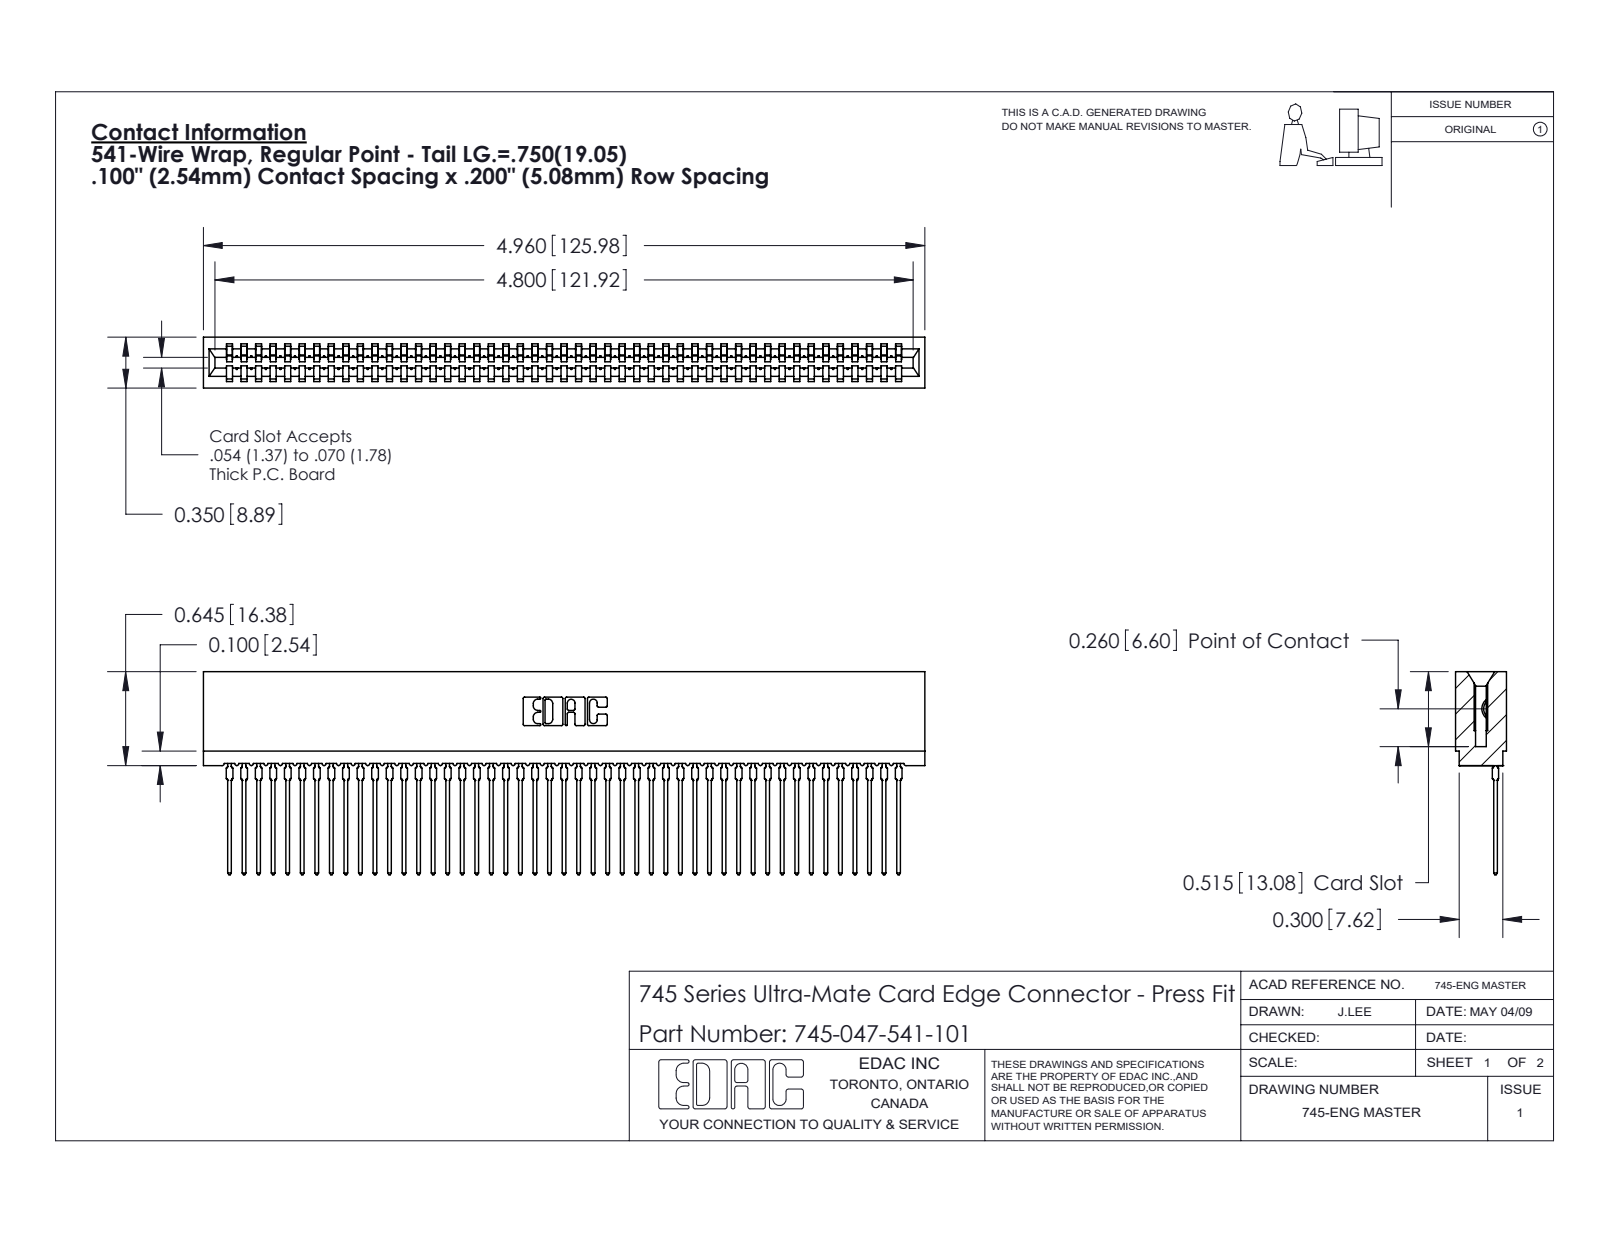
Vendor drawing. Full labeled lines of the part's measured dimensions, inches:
Part name (STEP PRODUCT): 745-047-541-101; 745 Part_Insulator Option - 01; 745-292-001_541
STEP written by: SolidWorks 2020 (CONFIG_CONTROL_DESIGN)
Units: inches
Bodies: 48 solids, 5359 faces (3204 planar, 933 cylindrical, 1222 other)
Overall size (bounding box): 4.96 × 1.396 × 0.35
Volume: 0.676 in³ · Surface area: 33.6 in²
Partial cylindrical surfaces — rounded edges, fillets, slot ends (radius × count): R0.015 ×94, R0.021 ×94, R0.01 ×22, R0.007 ×6, R0.031 ×6, R0.005 ×4, R0.011 ×4, R0.026 ×3
Main face-to-face distances: 0.35, 0.063, 0.287, 0.045, 0.305, 0.138, 0.212, 0.093, 0.167, 0.243
